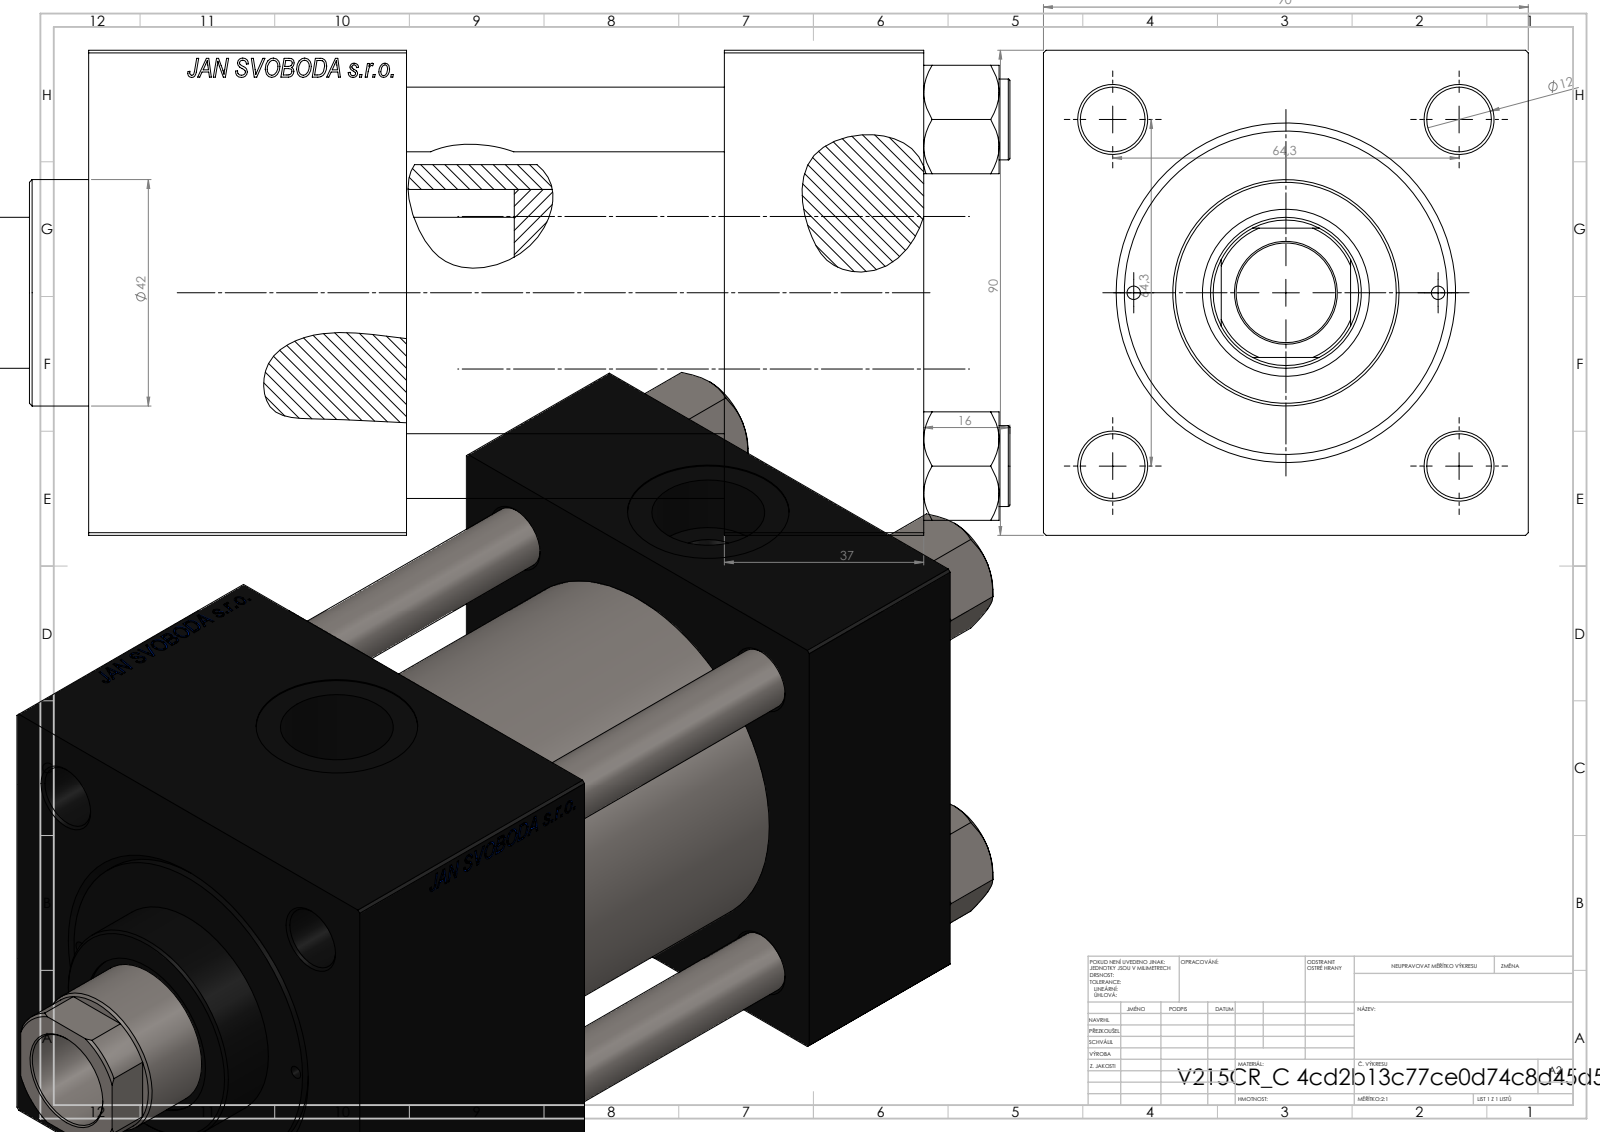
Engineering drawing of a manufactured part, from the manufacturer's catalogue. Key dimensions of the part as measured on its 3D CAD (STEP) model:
Part name (STEP PRODUCT): V215CR_C_Body; NUT_M5_C; V215_VC_A; V215CR_C_TYCINKA (+1 more)
STEP written by: SolidWorks 2019 (CONFIG_CONTROL_DESIGN)
Units: millimetres
Bodies: 11 solids, 1155 faces (528 planar, 91 cylindrical, 536 other)
Overall size (bounding box): 203 × 90 × 90
Volume: 946 713 mm³ · Surface area: 179 212 mm²
Round holes (diameter × count): ⌀12 ×4, ⌀2.5 ×2, ⌀7 ×2, ⌀20.96 ×2, ⌀30 ×2, ⌀18.5 ×1, ⌀28 ×1, ⌀31 ×1, ⌀50 ×1, ⌀60 ×1, ⌀63 ×1
Round bosses / shafts (diameter × count): ⌀15 ×4, ⌀69 ×1, ⌀42 ×1
Partial cylindrical surfaces — rounded edges, fillets, slot ends (radius × count): R13.5 ×1
Main face-to-face distances: 90, 59, 37, 155, 118, 96, 126.3, 89.3, 30.3, 28.7
Hole centre spacings: 32.39, 45.47, 64.3, 68.42, 28.25, 90.93, 56.5, 97.5
